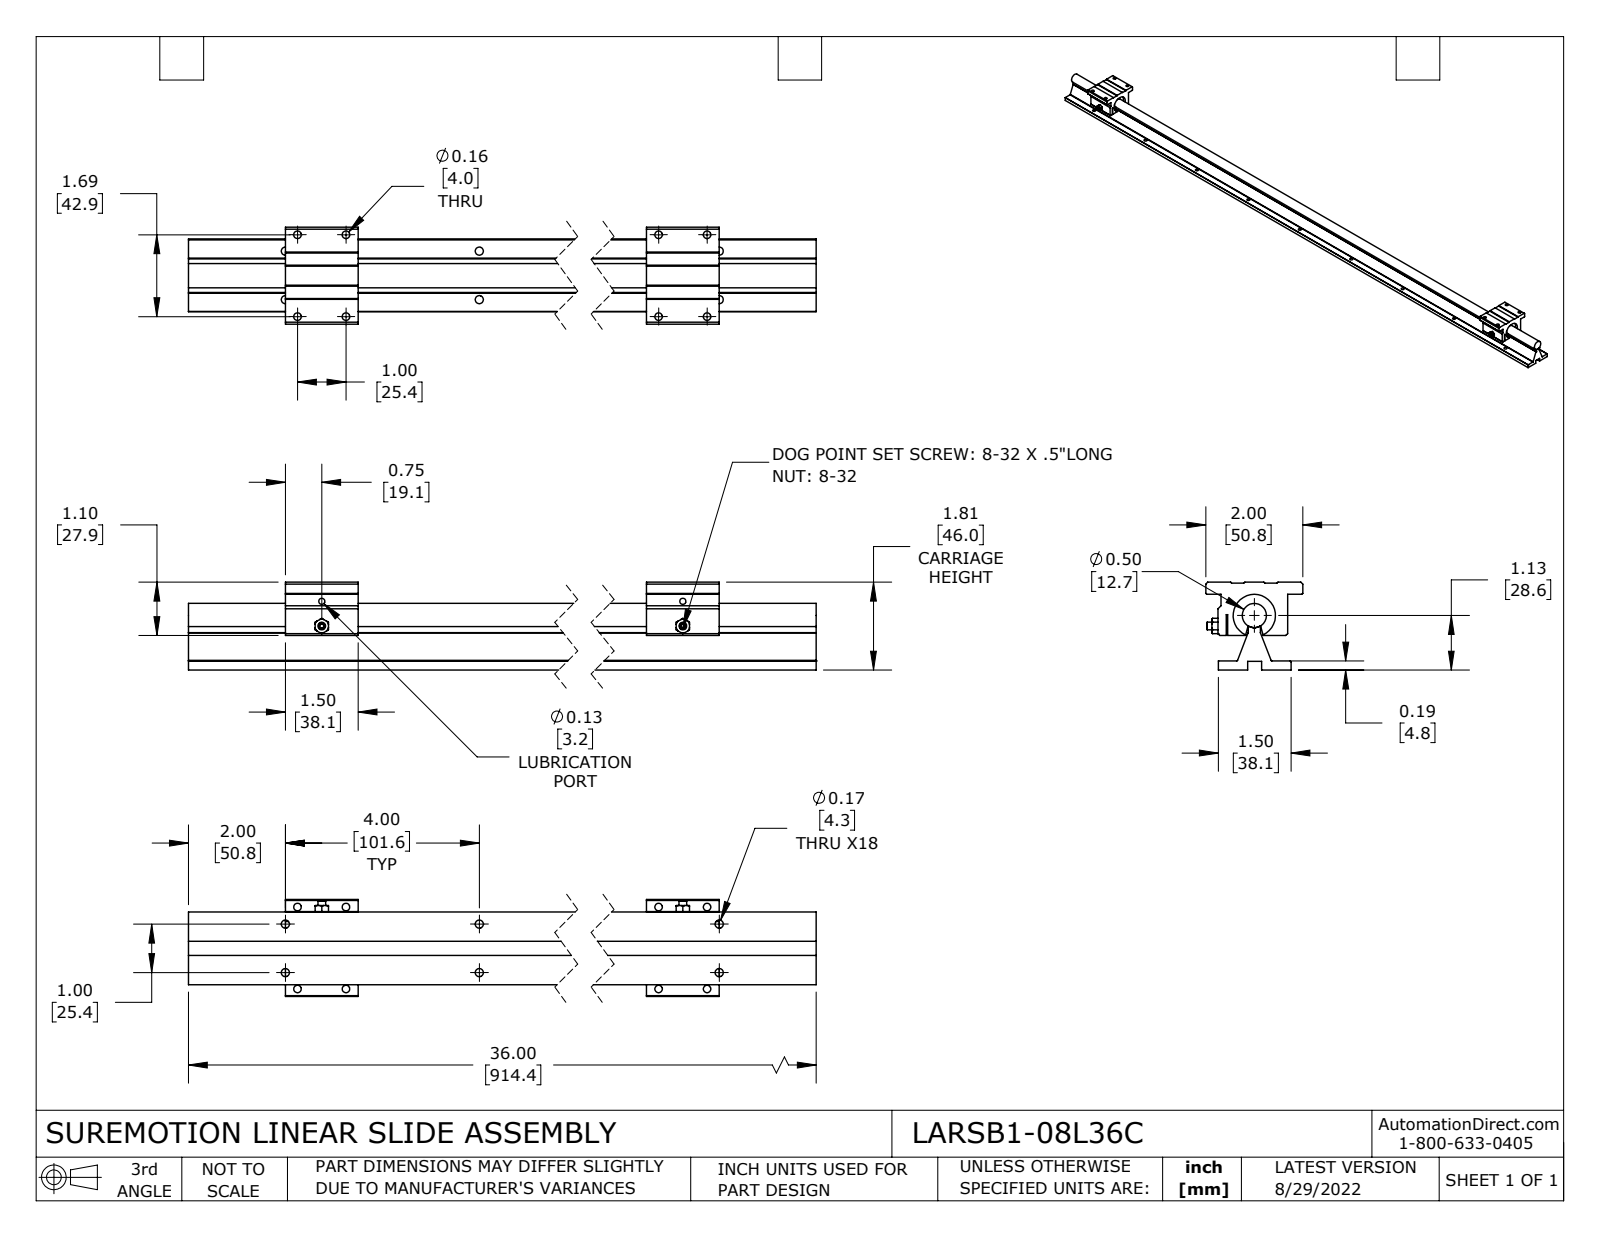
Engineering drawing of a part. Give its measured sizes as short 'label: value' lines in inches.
name: LARSACC-004; LARSB1-08L36C; LARSB1-08L36C-RAIL
written by: SolidWorks 2021 (CONFIG_CONTROL_DESIGN)
unit: in
bodies: 4 solids, 228 faces (119 planar, 93 cylindrical, 16 other)
size: 36 × 2 × 1.812
volume: 30.28 in³; area: 264.7 in²
holes: 18× ⌀0.169, 8× ⌀0.156, 2× ⌀0.126, 2× ⌀0.5, 2× ⌀0.874
bosses: 2× ⌀0.157
rounds: 8× R0.02, 1× R0.04, 1× R0.249
face distances: 0.187, 0.605, 0.895, 0.18, 1.5, 0.25, 0.29, 0.633, 0.883, 0.028
hole spacings: 4, 4.123, 8, 8.062, 1, 12, 12.042, 16
